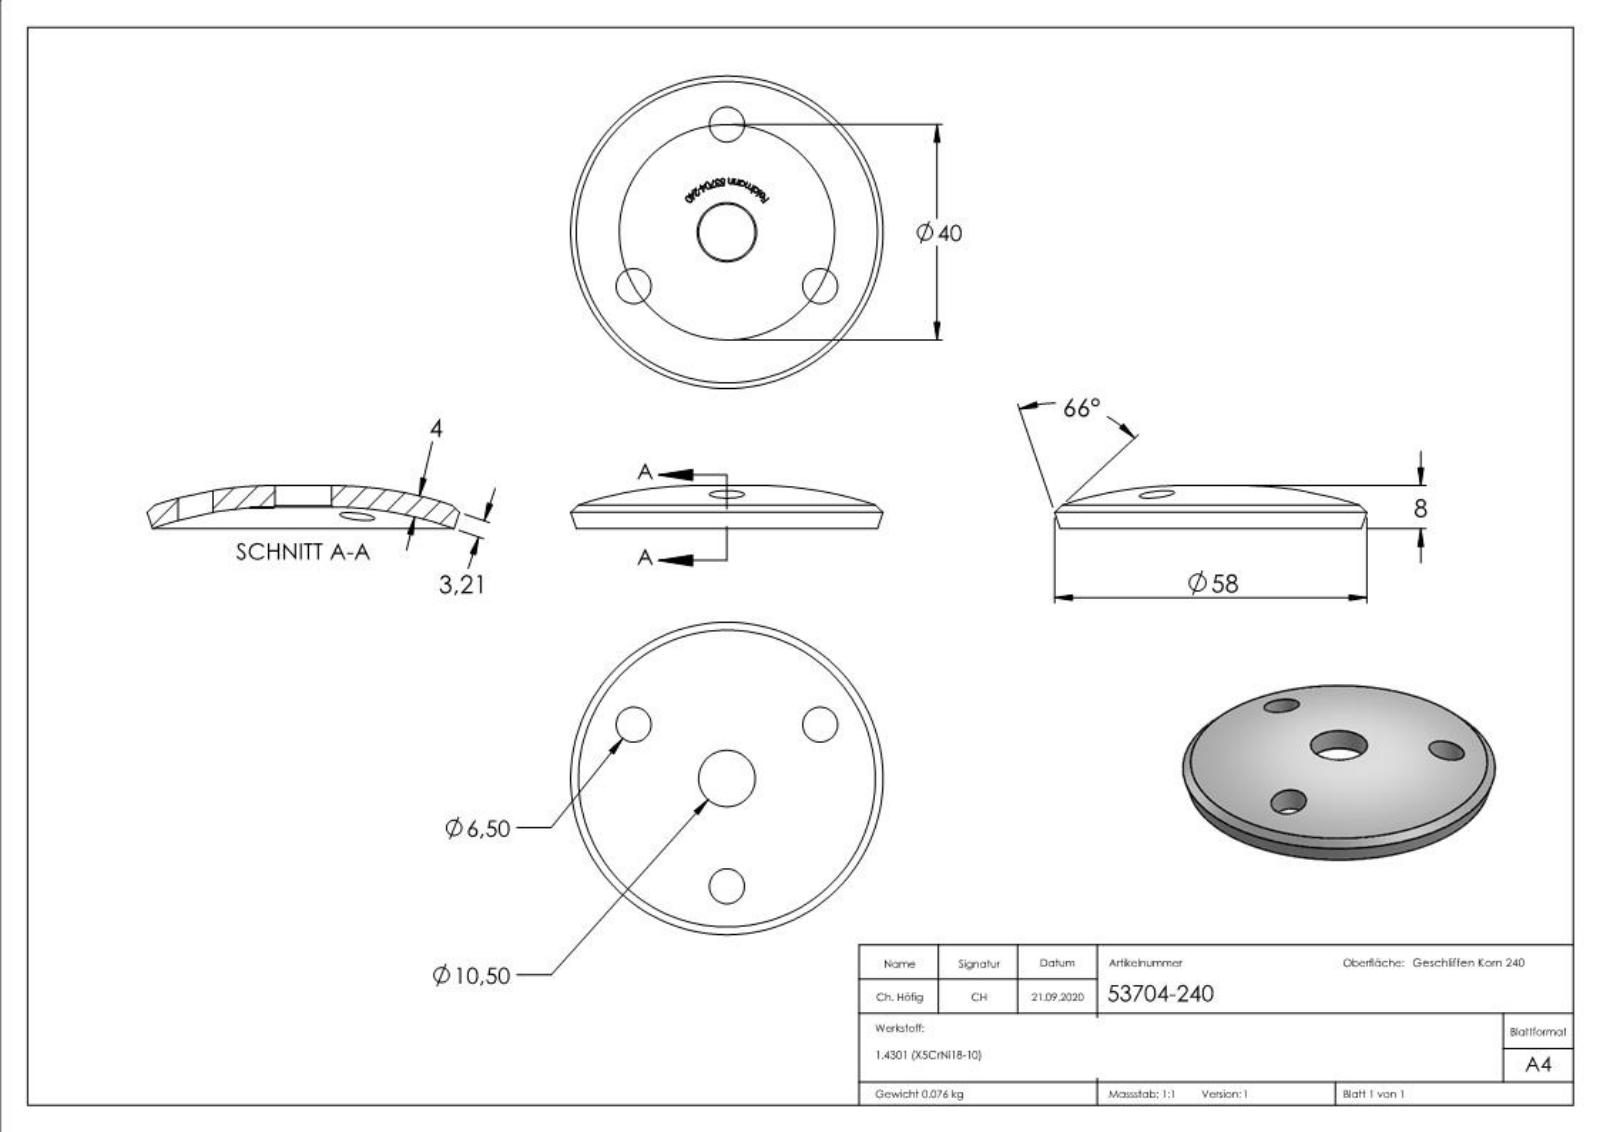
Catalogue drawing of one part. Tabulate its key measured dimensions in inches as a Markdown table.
| quantity | value |
| --- | --- |
| part name | 53704-240 |
| STEP written by | SolidWorks 2018 (CONFIG_CONTROL_DESIGN) |
| units | inches |
| bodies | 1 solid, 241 faces (105 planar, 8 cylindrical, 128 other) |
| overall size | 2.283 × 2.283 × 0.315 |
| volume | 0.591 in³ |
| surface area | 9.142 in² |
| round holes (diameter × count) | 0.256 × 3, 0.413 × 1 |
| main face-to-face distances | 0.021, 0.028, 0.033, 0.026, 0.052, 0.057, 0.047, 0.052, 0.026, 0.016 |
| hole center spacings | 0.787, 1.364 |
